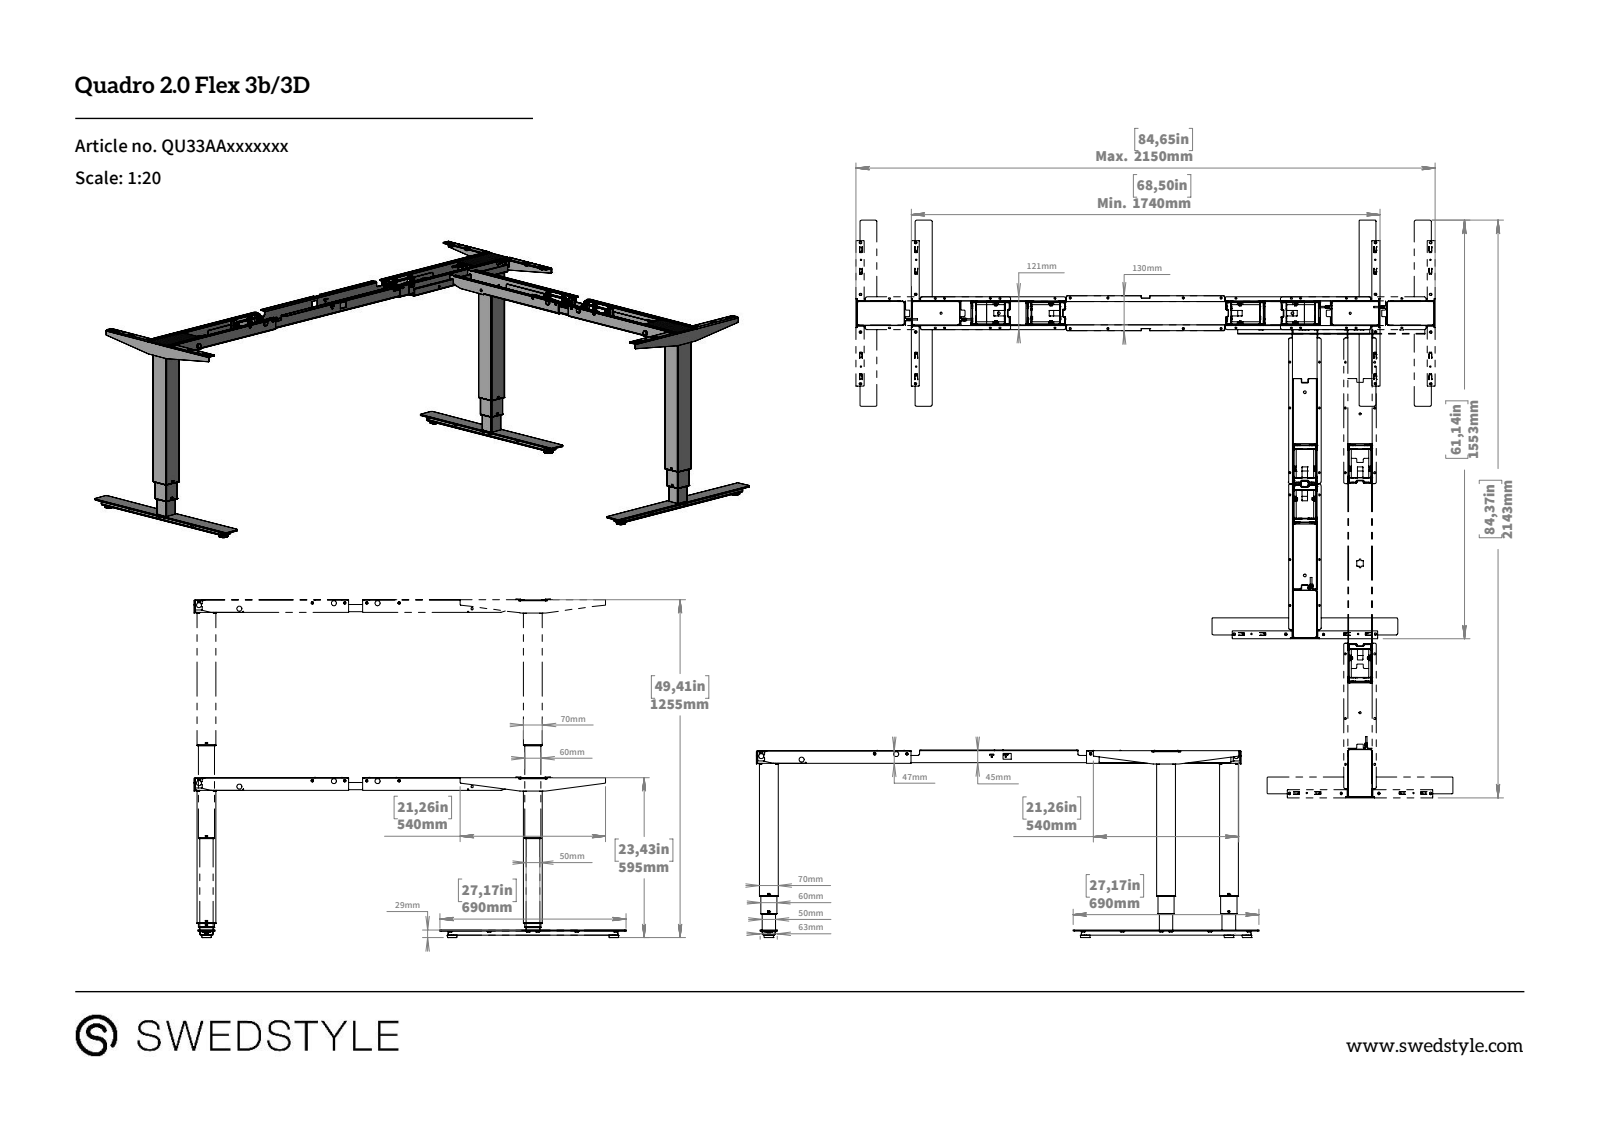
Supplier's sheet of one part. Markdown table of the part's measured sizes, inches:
| quantity | value |
| --- | --- |
| part name | QU33AAxxxxxxx_Fl174_Fl115 |
| STEP written by | SolidWorks 2015 (CONFIG_CONTROL_DESIGN) |
| units | inches |
| bodies | 0 solids, 2105 faces (1087 planar, 746 cylindrical, 272 other) |
| overall size | 73.465 × 63.106 × 27.35 |
| round holes (diameter × count) | 0.236 × 13, 0.63 × 12, 0.315 × 7, 0.551 × 6, 0.197 × 5, 0.276 × 4, 0.394 × 3, 0.335 × 1 |
| round bosses / shafts (diameter × count) | 0.335 × 3, 0.217 × 3, 0.315 × 2 |
| partial cylindrical surfaces (radius × count) | 0.02 × 115, 0.098 × 86, 0.079 × 44, 0.039 × 39, 0.157 × 36, 0.118 × 31, 0.108 × 26, 0.197 × 24 |
| main face-to-face distances | 0.079, 0.157, 0.098, 24.492, 3.563, 0.02, 2.756, 0.394, 3.661, 0.315 |
| hole center spacings | 5.512, 7.108, 11.024, 11.902, 4.488, 16.535, 17.134, 24.342 |
